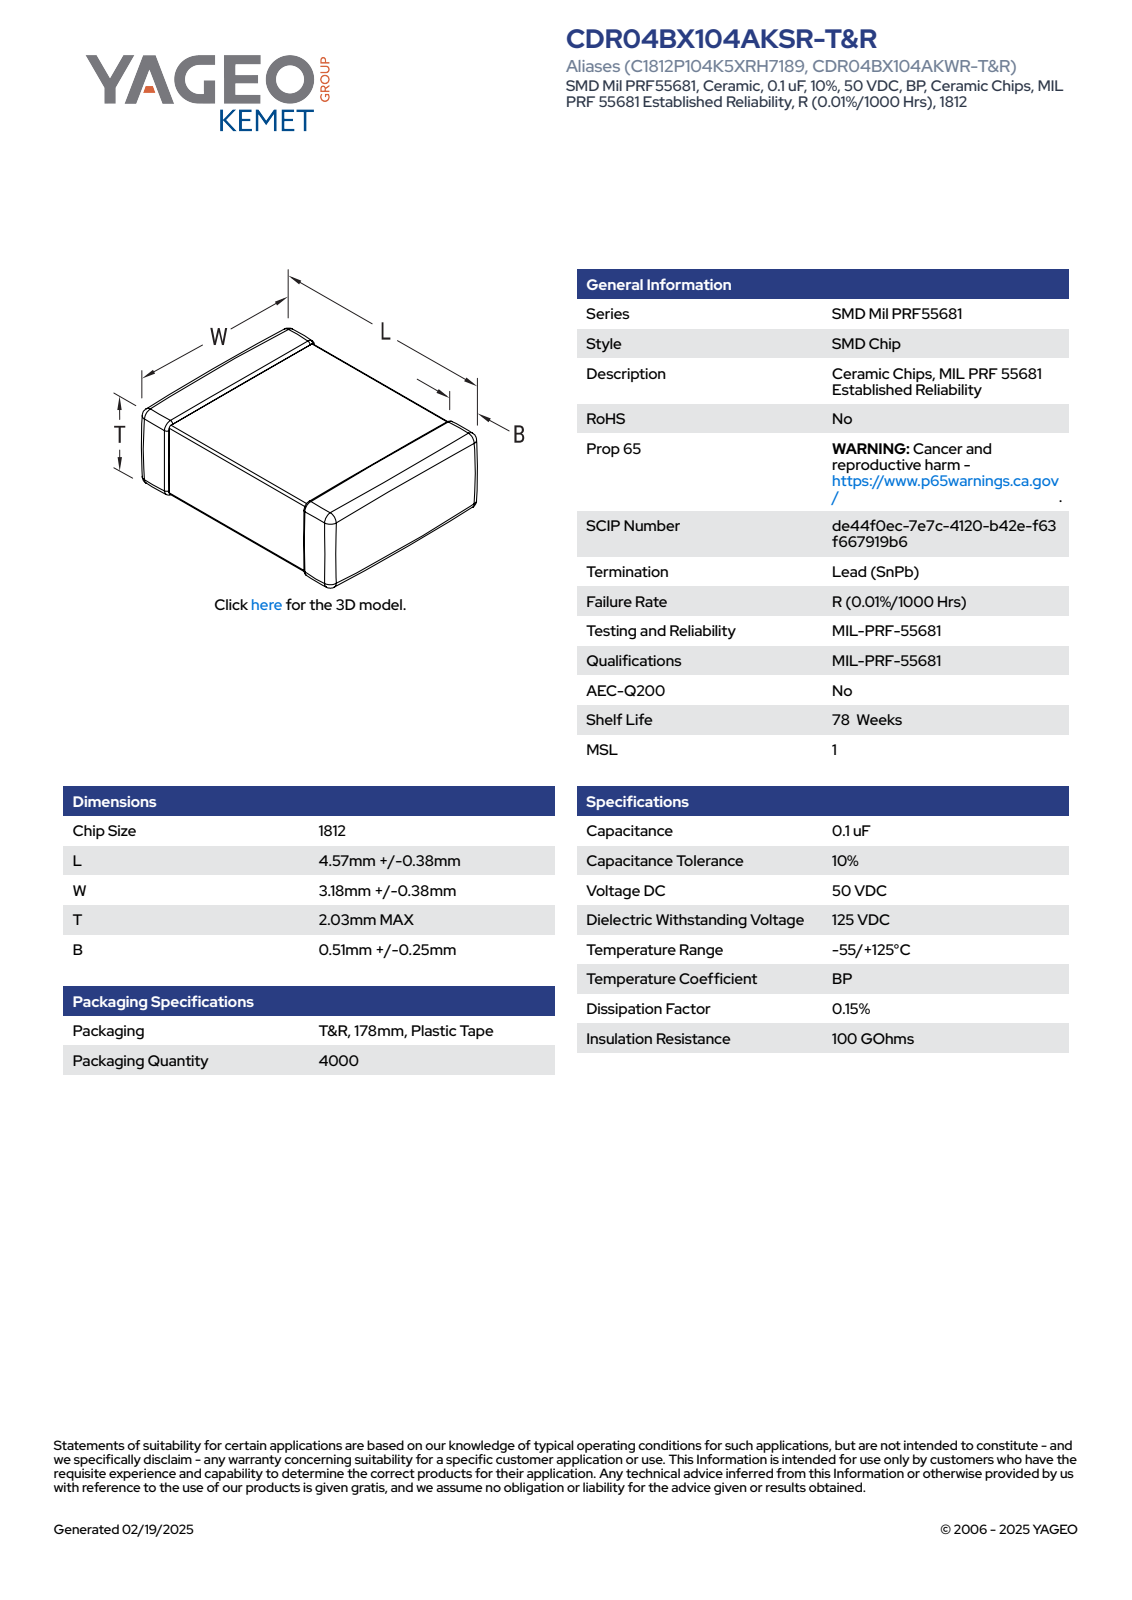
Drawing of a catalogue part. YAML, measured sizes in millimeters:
part_name: "CCS_STDNOS_1812_L5.59W3.94T2.41B0.51"
step_written_by: "SolidWorks 2014 (AUTOMOTIVE_DESIGN)"
units: millimeters
bodies: {solids: 4, faces: 125, planar: 71, cylindrical: 38, other: 16}
overall_size: [5.59, 3.94, 2.41]
volume: 48
surface_area: 89
face_to_face_distances: [2.25, 3.78, 5.59, 2.33, 3.86, 2.41, 3.94, 0.6, 1.66, 1.58]
